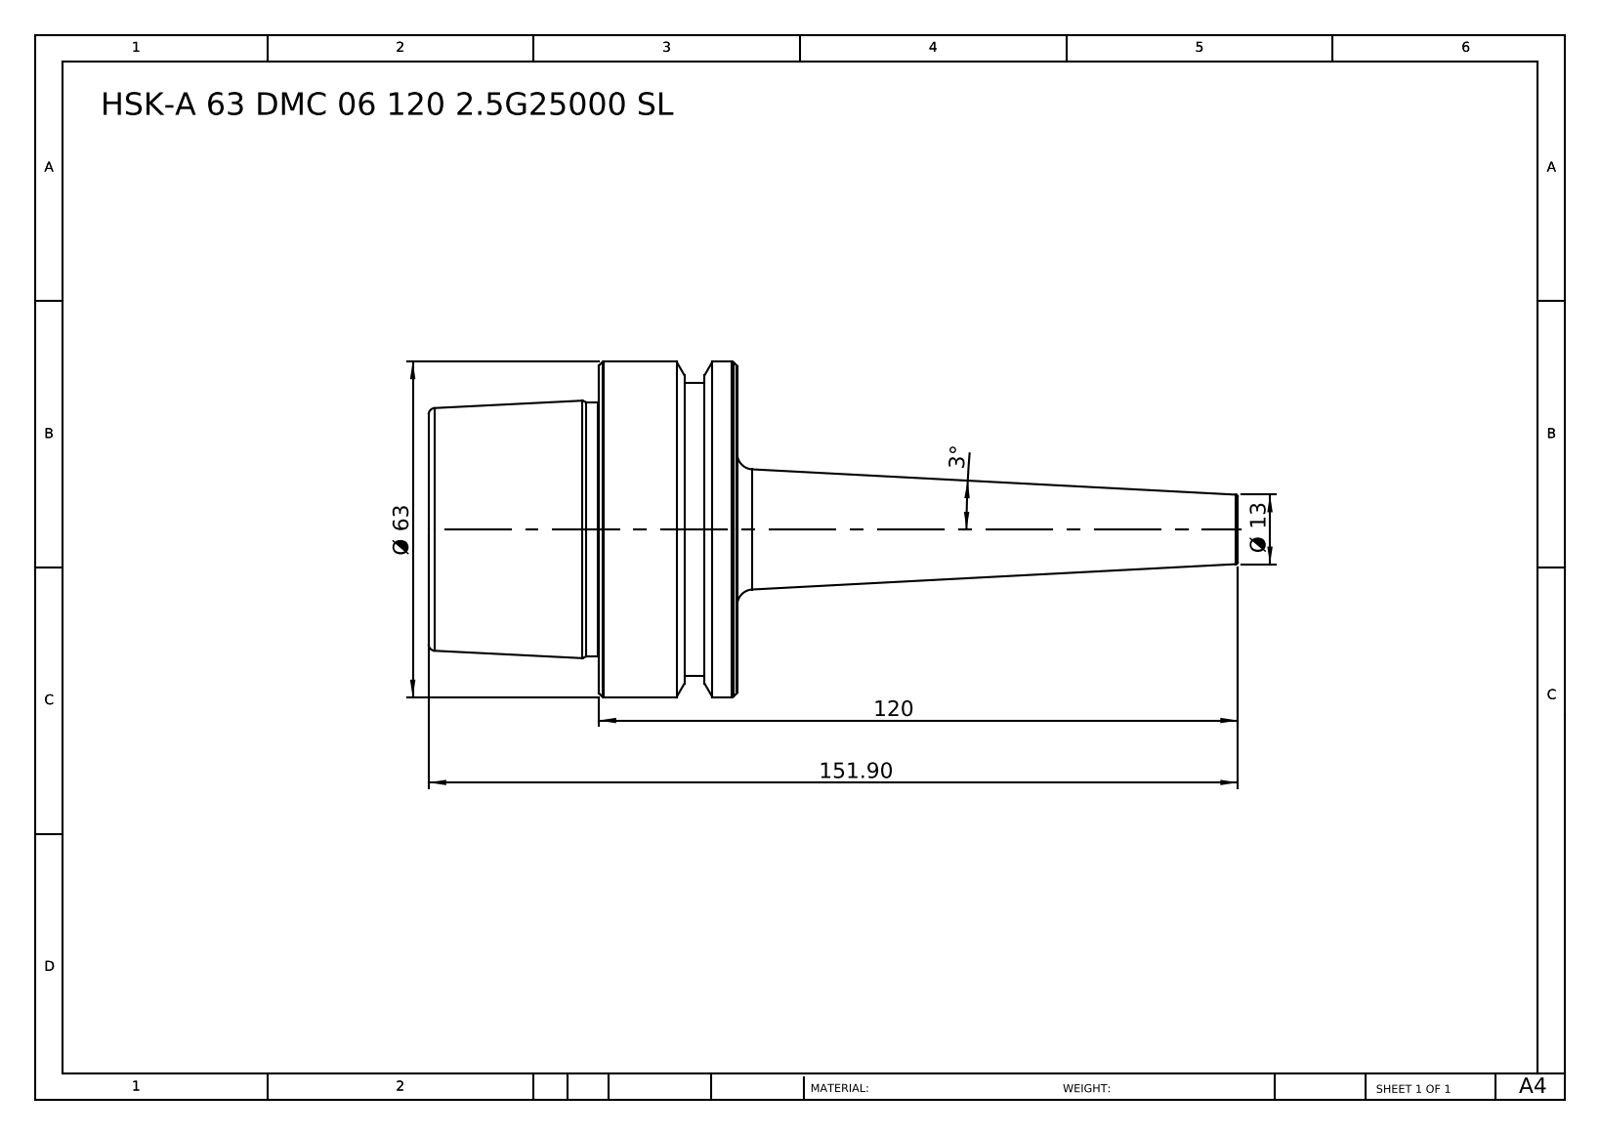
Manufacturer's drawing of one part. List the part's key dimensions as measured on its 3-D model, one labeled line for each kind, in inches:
Part name (STEP PRODUCT): HSK-A 63 DMC 06 120 2.5G25000 SL
STEP written by: SolidWorks 2014 (CONFIG_CONTROL_DESIGN)
Units: inches
Bodies: 1 solid, 46 faces (6 planar, 8 cylindrical, 32 other)
Overall size (bounding box): 5.98 × 2.48 × 2.48
Volume: 9.582 in³ · Surface area: 33.46 in²
Round bosses / shafts (diameter × count): ⌀2.48 ×1, ⌀2.165 ×1, ⌀1.881 ×1
Main face-to-face distances: 2.28, 1.024, 1.256, 0.24, 0.783, 2.039, 0.39, 0.15, 0.634, 1.89
